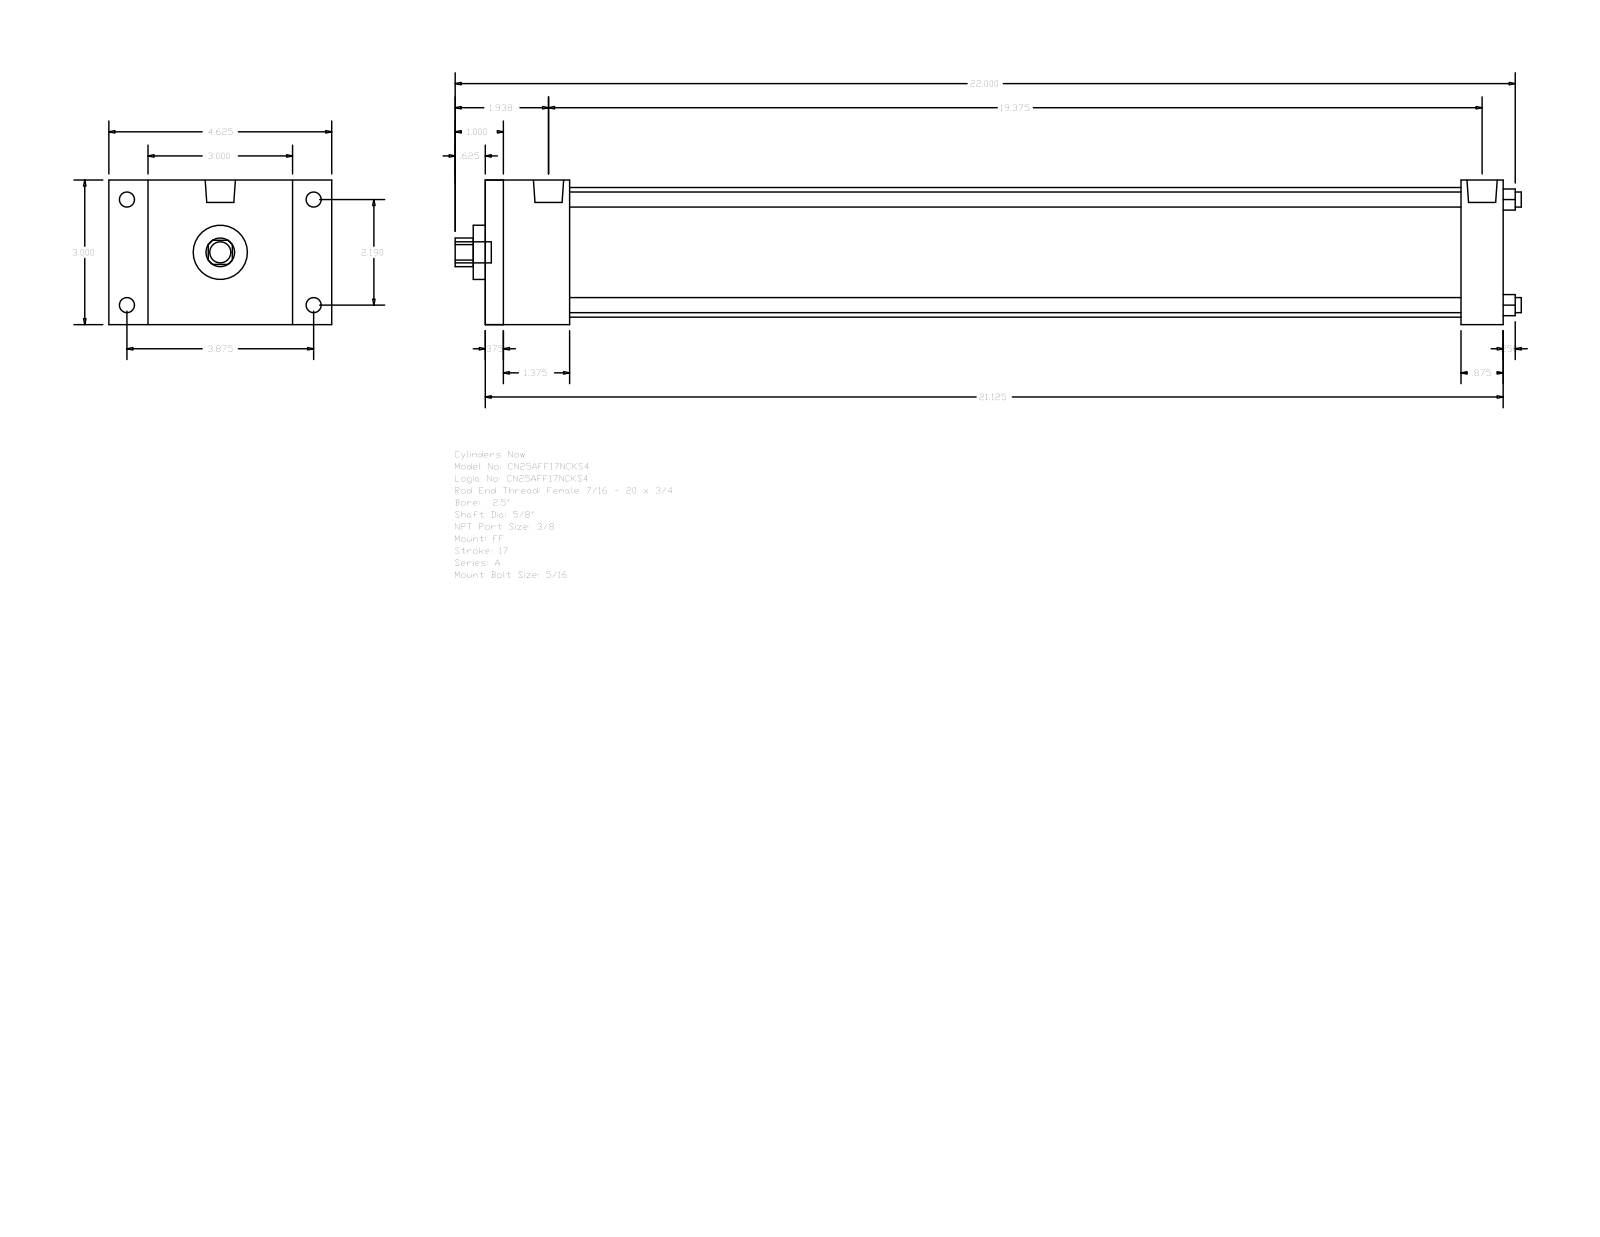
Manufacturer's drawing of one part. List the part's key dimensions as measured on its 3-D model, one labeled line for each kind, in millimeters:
Part name (STEP PRODUCT): A_FF__0250_0.625
STEP written by: GSSL Pune (CONFIG_CONTROL_DESIGN)
Units: millimetres
Bodies: 0 solids, 92 faces (64 planar, 28 cylindrical, 0 other)
Overall size (bounding box): 561.98 × 117.47 × 76.2
Round holes (diameter × count): ⌀7.94 ×4, ⌀15.88 ×1, ⌀28.57 ×1, ⌀68.33 ×1
Round bosses / shafts (diameter × count): ⌀7.94 ×4, ⌀5.56 ×4, ⌀15.93 ×2, ⌀11.11 ×1
Partial cylindrical surfaces — rounded edges, fillets, slot ends (radius × count): R7.54 ×1
Main face-to-face distances: 76.2, 536.57, 9.52, 527.05, 44.45, 514.35, 34.93, 504.83, 469.9, 492.12
Hole centre spacings: 39.33, 55.62, 78.66
